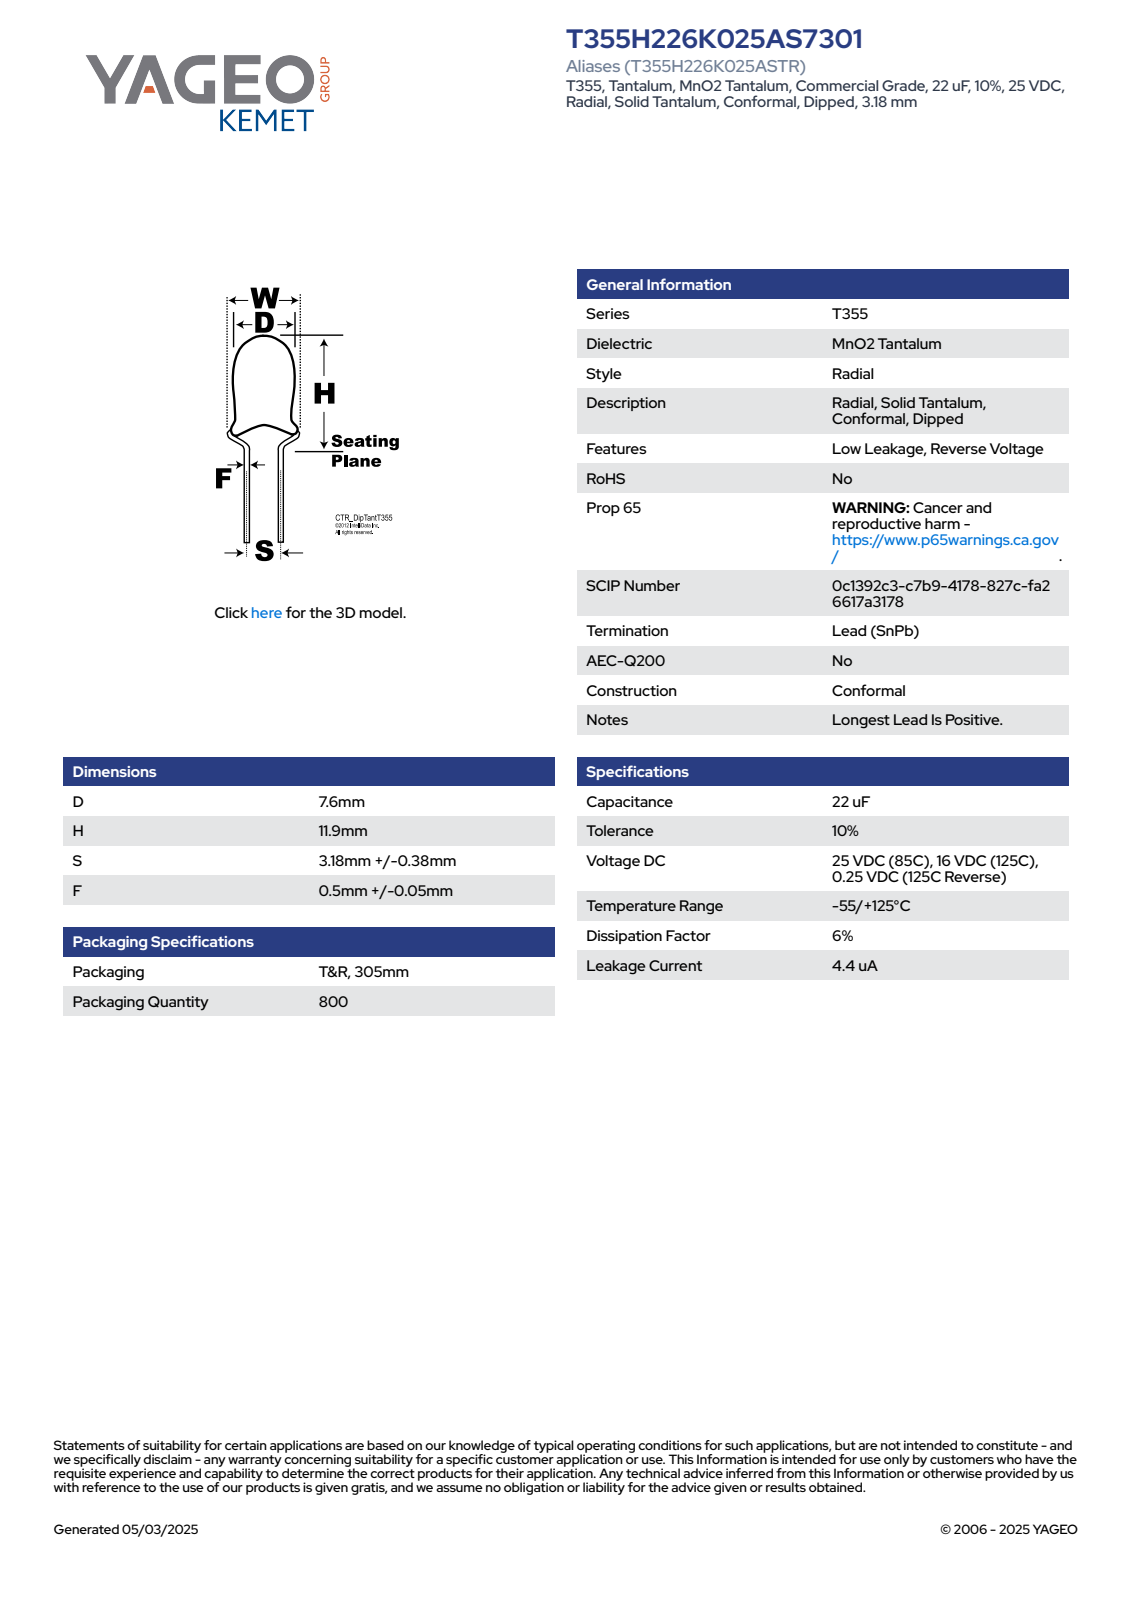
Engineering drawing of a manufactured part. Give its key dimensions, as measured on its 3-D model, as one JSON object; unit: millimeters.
{"part_name": "CTR_T355_D7.6W6.99H11.9S3.18LL5.56F0.55", "step_written_by": "SolidWorks 2021 (AUTOMOTIVE_DESIGN)", "units": "millimeters", "bodies": {"solids": 1, "faces": 104, "planar": 30, "cylindrical": 6, "other": 68}, "overall_size": [17.46, 7.6, 7.6], "volume_mm3": 310, "surface_area_mm2": 265, "round_bosses_or_shafts": [[7.6, 1]], "partial_cylinders_radius": [[3.79, 1]], "face_to_face_distances": [8.3, 9.16, 17.46, 13.47, 4.31, 3.99, 12.86, 3.7, 0.61, 4.6]}
